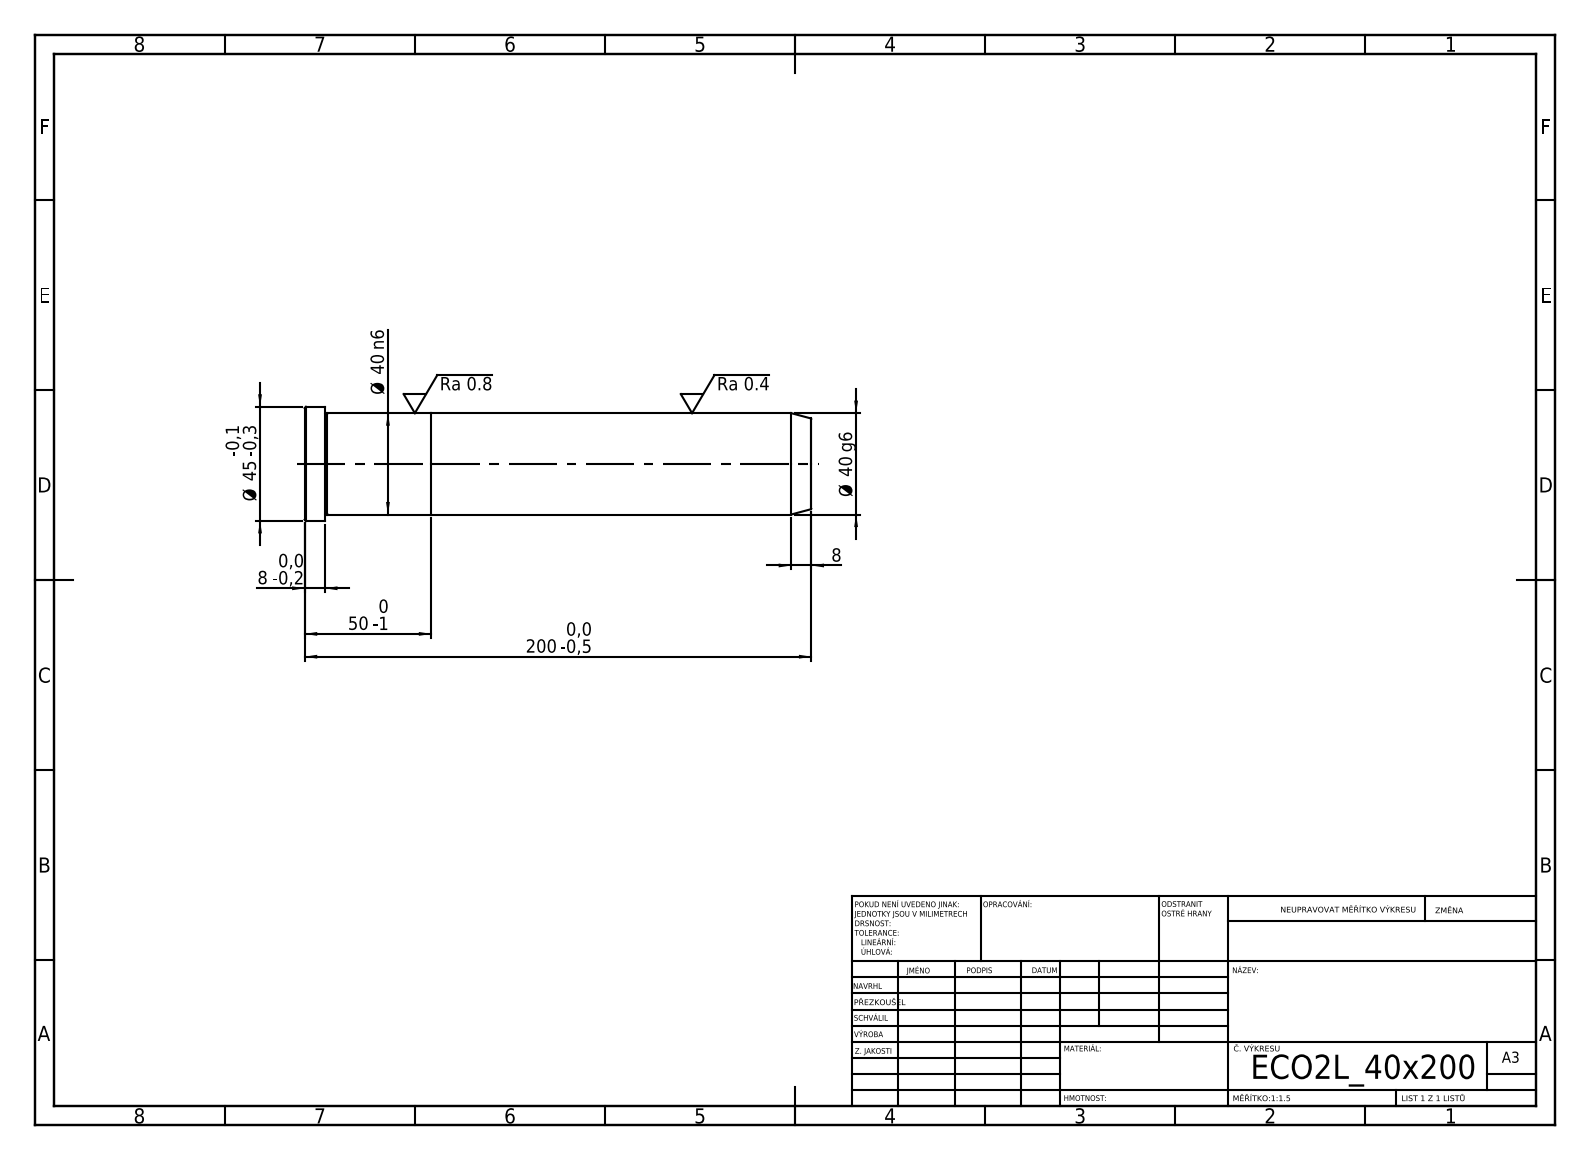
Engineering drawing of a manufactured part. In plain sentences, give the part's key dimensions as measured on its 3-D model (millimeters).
Its 3-D file was written by "SolidWorks 2019 (CONFIG_CONTROL_DESIGN)". It is 2 solids with 21 faces: 5 planar, 6 cylindrical and 10 other. Overall it measures 200 by 45 by 45 millimeters. Its volume is 252 889 cubic millimeters and its surface area 30 691 square millimeters. Round bosses or shafts: 1 of diameter 45, 1 of diameter 40. The main face-to-face distances are 50, 150, 200, 192, 42, 8.
